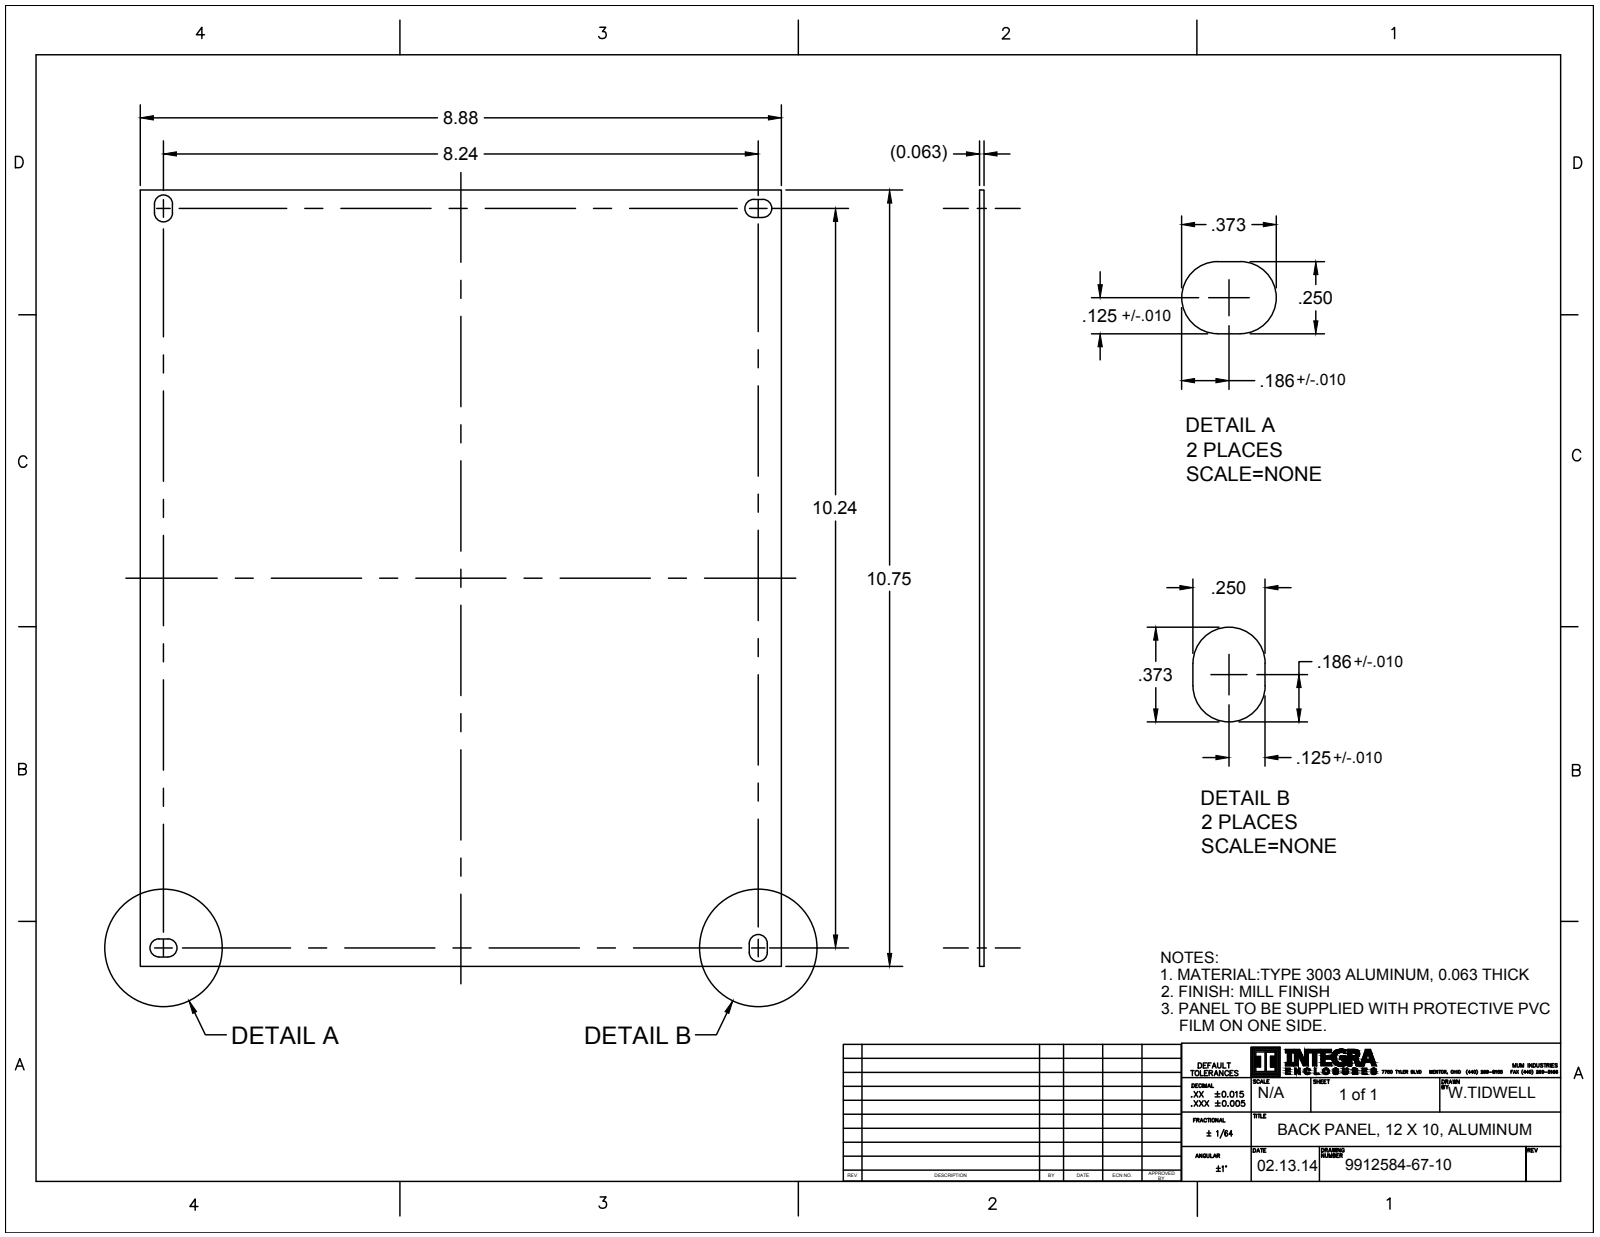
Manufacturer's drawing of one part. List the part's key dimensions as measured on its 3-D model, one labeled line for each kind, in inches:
Part name (STEP PRODUCT): 9912584-67-10; 9912518-82-10; ABP1210_ASM
STEP written by: CREO PARAMETRIC BY PTC INC, 2016050 (CONFIG_CONTROL_DESIGN)
Units: inches
Bodies: 5 solids, 430 faces (90 planar, 268 cylindrical, 72 other)
Overall size (bounding box): 10.75 × 8.88 × 0.443
Volume: 6.062 in³ · Surface area: 195.5 in²
Round bosses / shafts (diameter × count): ⌀0.373 ×4, ⌀0.19 ×4, ⌀0.149 ×4
Partial cylindrical surfaces — rounded edges, fillets, slot ends (radius × count): R0.004 ×48, R0.125 ×8
Main face-to-face distances: 0.063, 8.88, 10.75, 0.25, 0.313, 0.25, 8.207, 10.199, 0.333, 0.083
